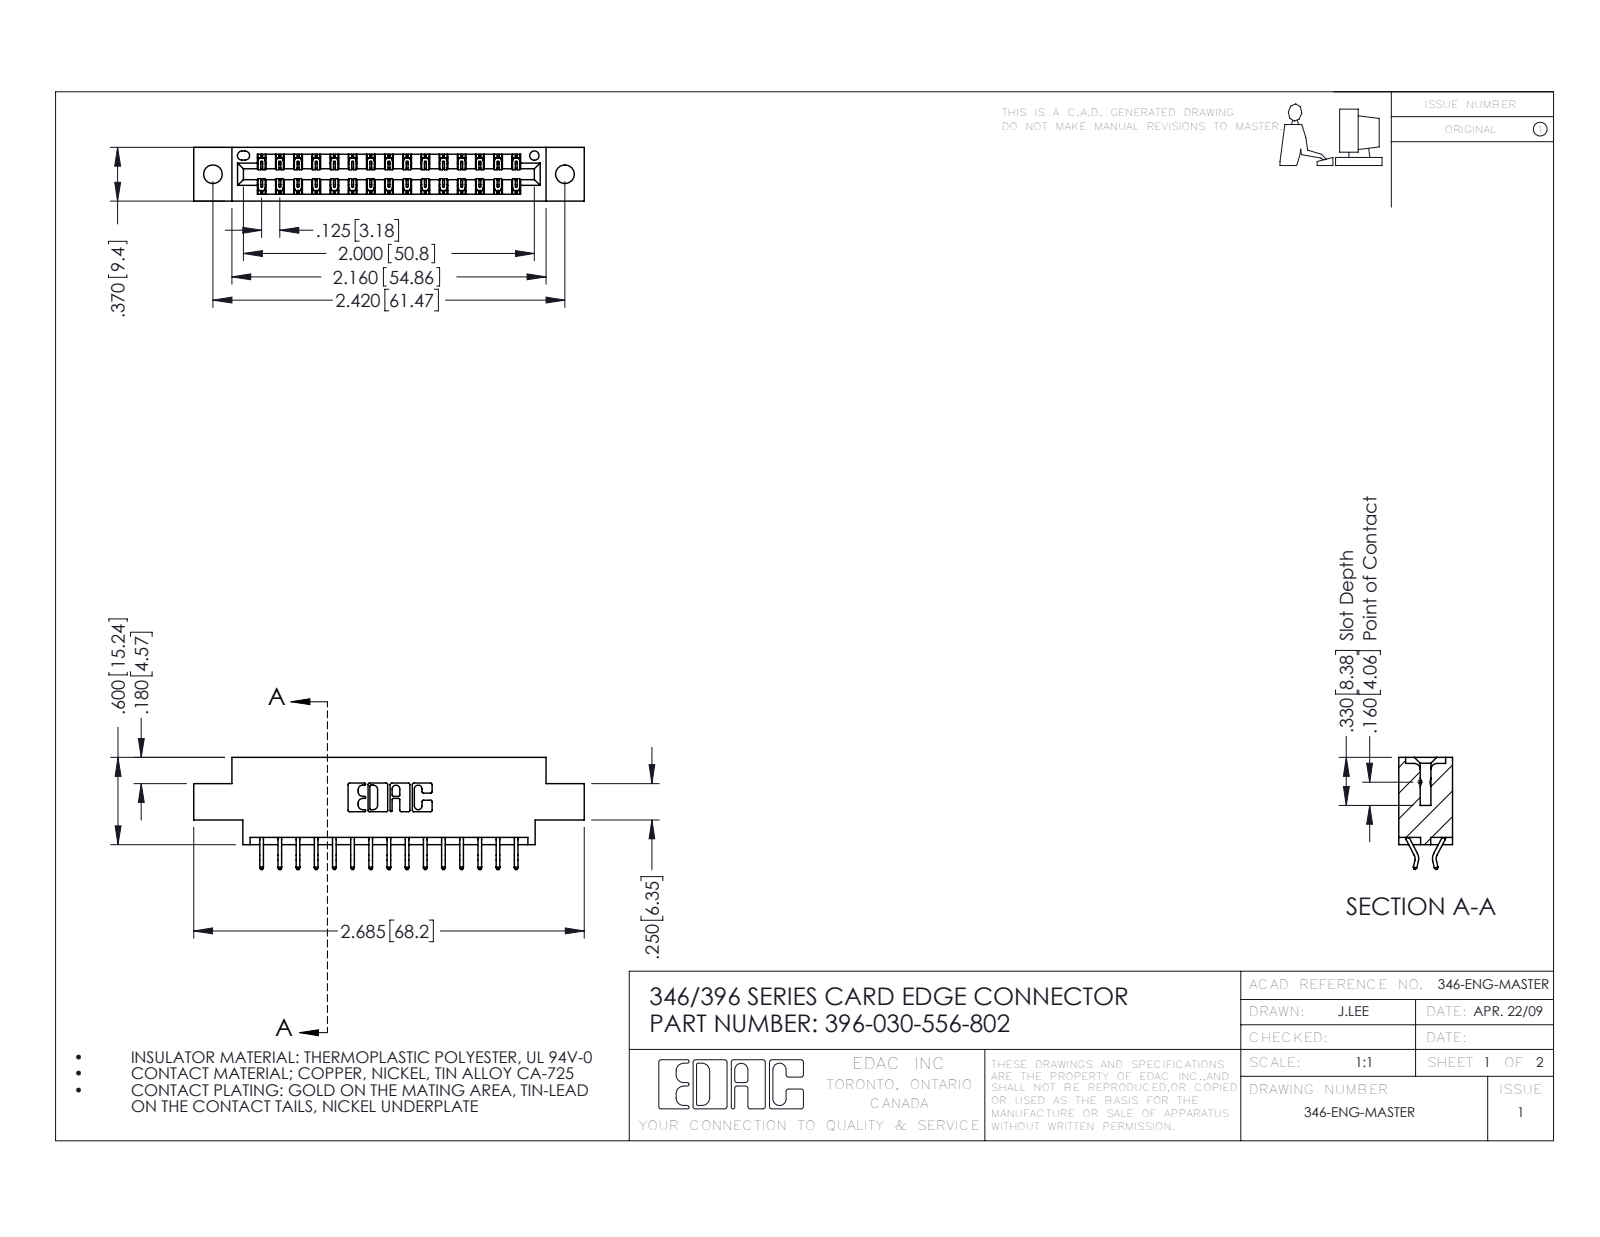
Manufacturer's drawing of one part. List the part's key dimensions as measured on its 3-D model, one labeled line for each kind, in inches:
Part name (STEP PRODUCT): 396-030-556-802; 345-292-001_556 Tail; 346 Part_0.170 Offset - 0.128 Dia
STEP written by: SolidWorks 2016 (CONFIG_CONTROL_DESIGN)
Units: inches
Bodies: 31 solids, 1866 faces (1250 planar, 616 cylindrical, 0 other)
Overall size (bounding box): 2.685 × 0.77 × 0.37
Volume: 0.381 in³ · Surface area: 12.47 in²
Round holes (diameter × count): ⌀0.128 ×2, ⌀0.064 ×1
Partial cylindrical surfaces — rounded edges, fillets, slot ends (radius × count): R0.006 ×45, R0.01 ×22, R0.007 ×6, R0.031 ×6, R0.026 ×3, R0.01 ×2, R0.014 ×2, R0.022 ×2
Main face-to-face distances: 0.048, 0.322, 0.37, 0.25, 0.025, 0.072, 0.298, 0.275, 0.148, 0.222
Hole centre spacings: 0.246, 2.213, 2.42
